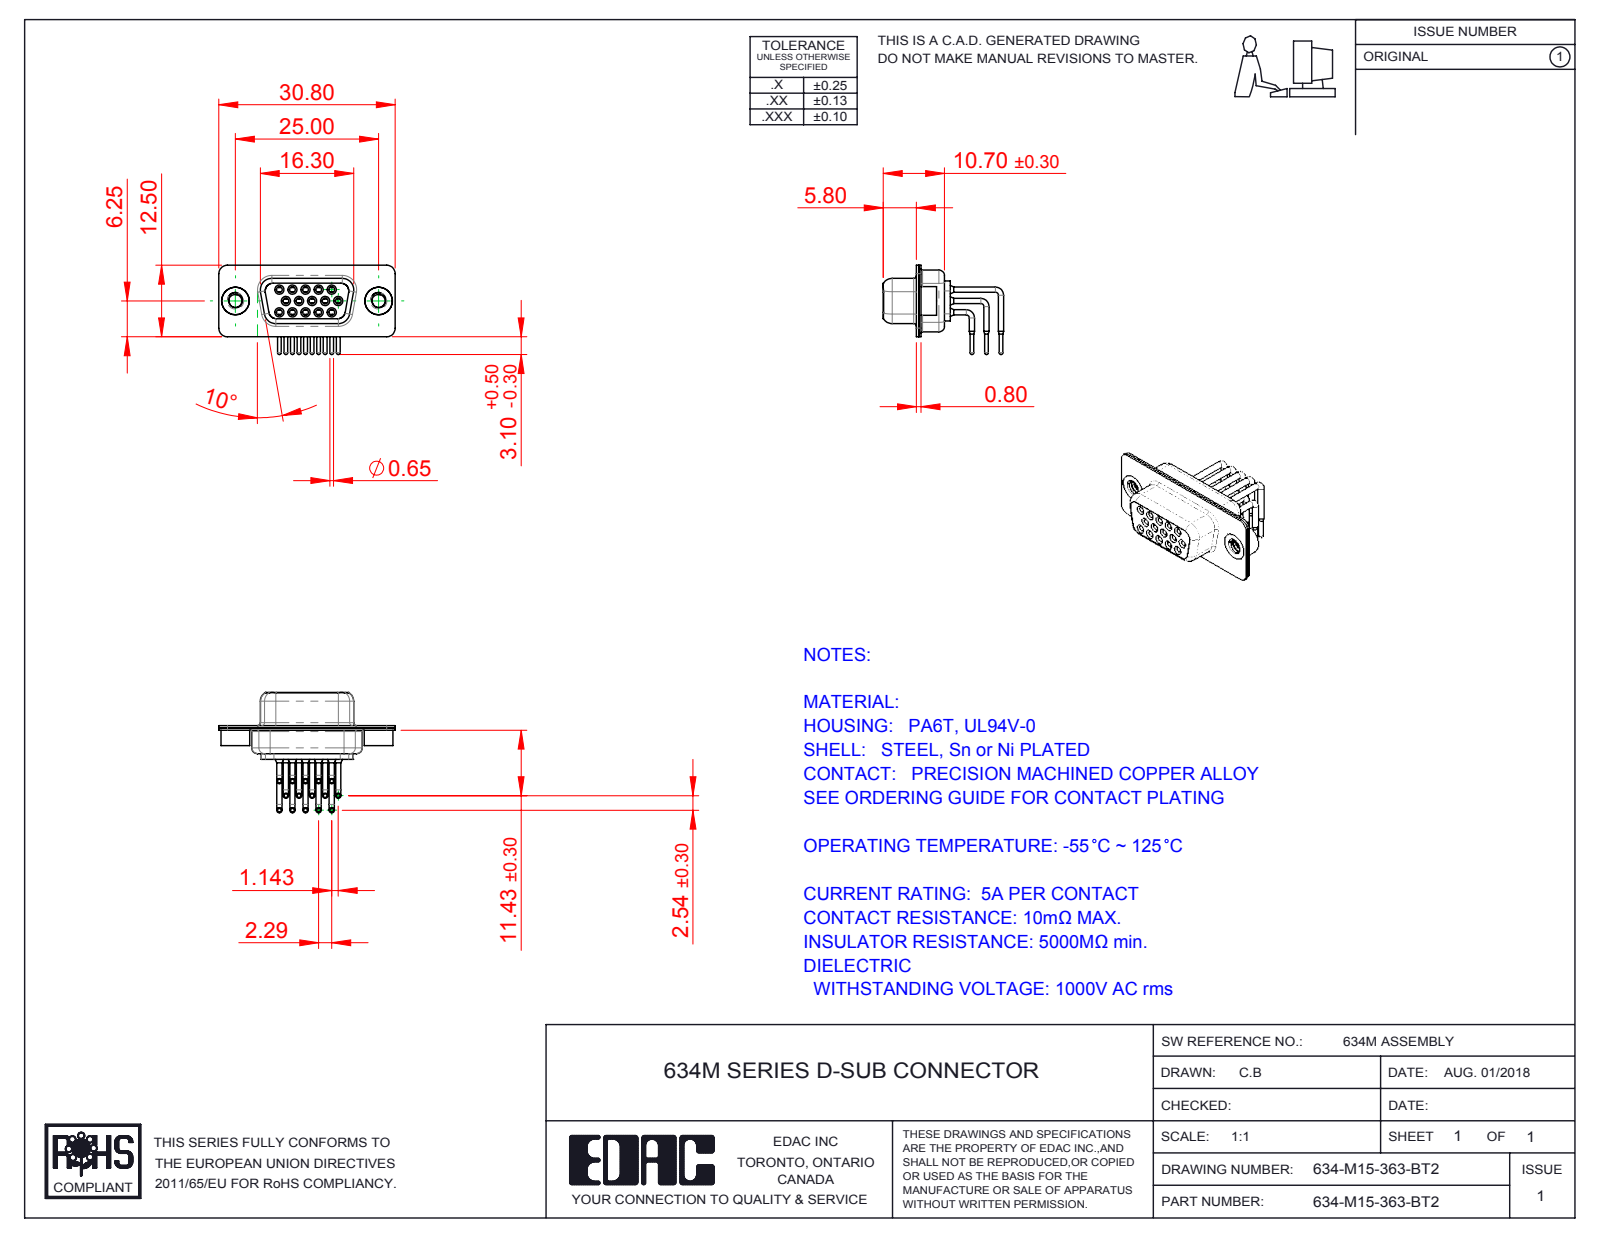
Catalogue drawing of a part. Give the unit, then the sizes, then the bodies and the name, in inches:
Units: inches
Overall size (bounding box): 1.213 × 0.828 × 0.614
Round holes (diameter × count): ⌀0.039 ×15, ⌀0.043 ×15, ⌀0.067 ×15, ⌀0.071 ×15, ⌀0.079 ×15, ⌀0.089 ×2, ⌀0.157 ×2, ⌀0.189 ×2
Round bosses / shafts (diameter × count): ⌀0.035 ×30, ⌀0.063 ×15, ⌀0.059 ×15, ⌀0.026 ×15, ⌀0.197 ×2, ⌀0.193 ×2, ⌀0.079 ×1
Partial cylindrical surfaces — rounded edges, fillets, slot ends (radius × count): R0.059 ×16, R0.079 ×12, R0.053 ×8, R0.063 ×8, R0.01 ×4, R0.02 ×4, R0.024 ×4, R0.026 ×4
Main face-to-face distances: 0.016, 0.031, 0.091, 0.057, 0.352, 0.075, 0.335, 0.033, 0.244, 0.368
Hole centre spacings: 0.09, 0.156, 0.09, 0.18, 0.238, 0.238, 0.27, 0.312
Volume: 0.106 in³ · Surface area: 8.796 in²
Bodies: 20 solids, 1074 faces (292 planar, 482 cylindrical, 300 other)
Part name (STEP PRODUCT): 634M Contact Row 3; 634M Housing_15 Contacts; 634M Shell Front_15 Contacts; 634M Contact Row 1 (+4 more)
STEP written by: SolidWorks 2016 (CONFIG_CONTROL_DESIGN)
